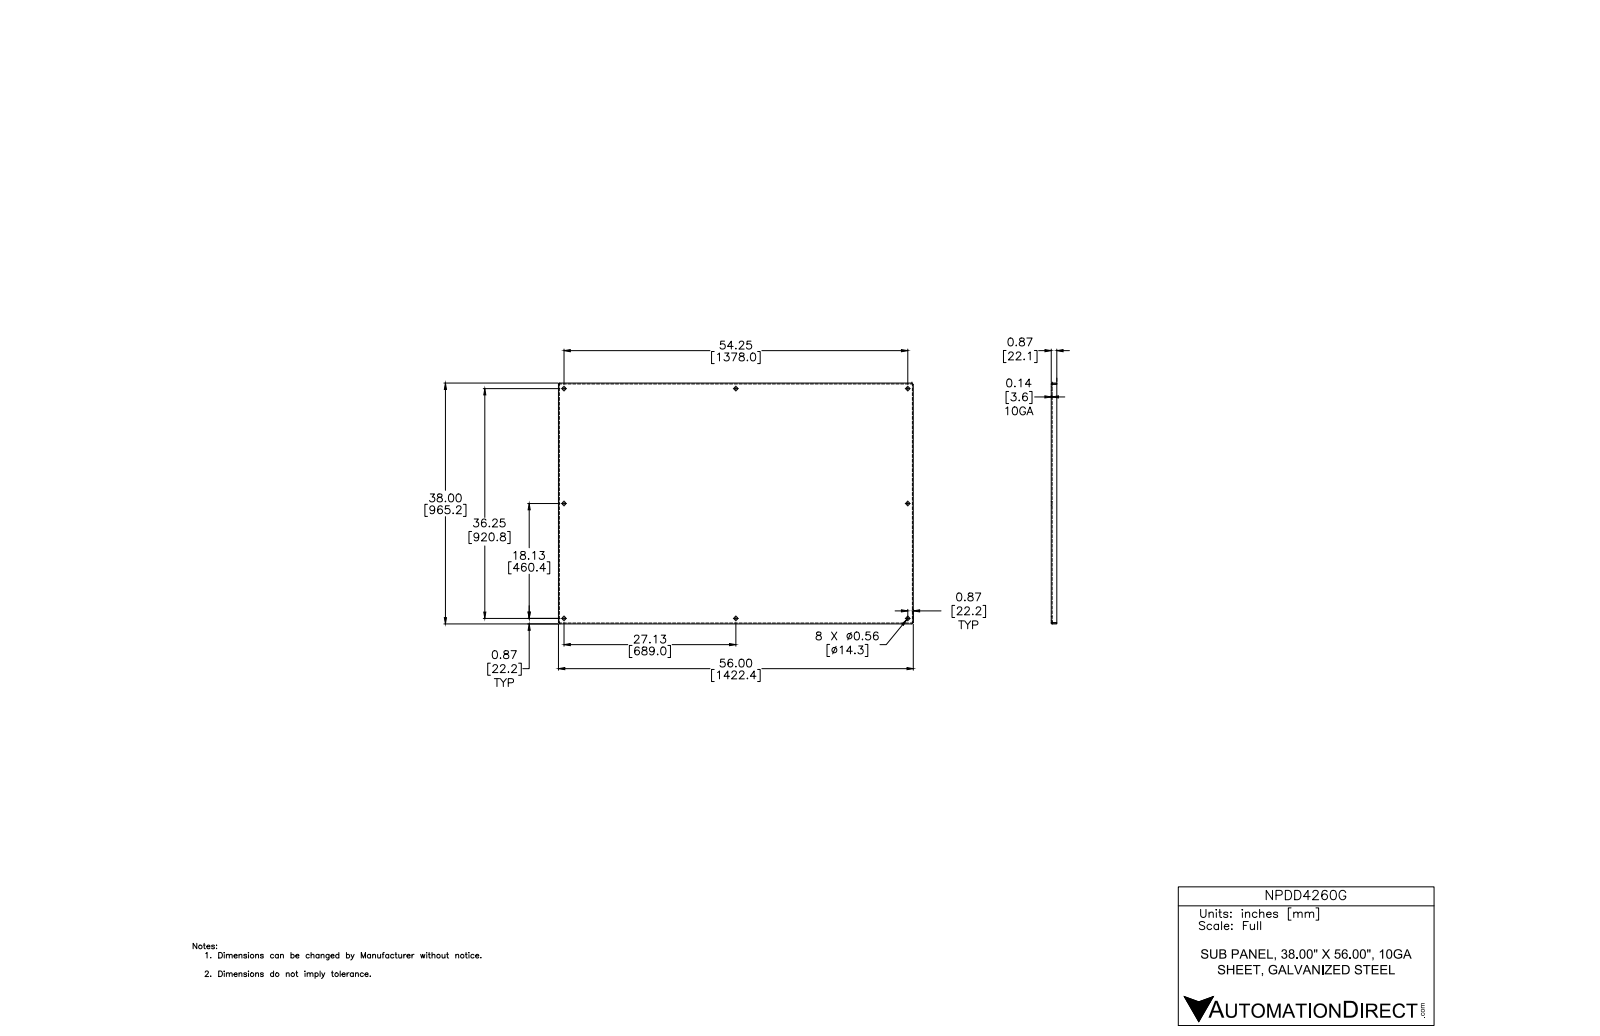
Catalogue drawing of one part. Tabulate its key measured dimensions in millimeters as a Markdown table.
| quantity | value |
| --- | --- |
| part name | NPDD4242G-NPDD7272G |
| STEP written by | Autodesk Inventor 2012 (AUTOMOTIVE_DESIGN) |
| units | millimeters |
| bodies | 1 solid, 46 faces (22 planar, 16 cylindrical, 8 other) |
| overall size | 1422.4 × 965.2 × 22.2 |
| volume | 4 626 000 mm³ |
| surface area | 2 930 000 mm² |
| round holes (diameter × count) | 14.3 × 8 |
| partial cylindrical surfaces (radius × count) | 0.8 × 4, 4 × 4 |
| main face-to-face distances | 3.2, 3.2, 962, 965.2, 958.9, 962, 1419.2, 1422.4, 1416.1, 1419.2 |
| hole center spacings | 689, 1452.8, 460.4, 1150, 1378, 828.6, 828.6, 920.8 |
